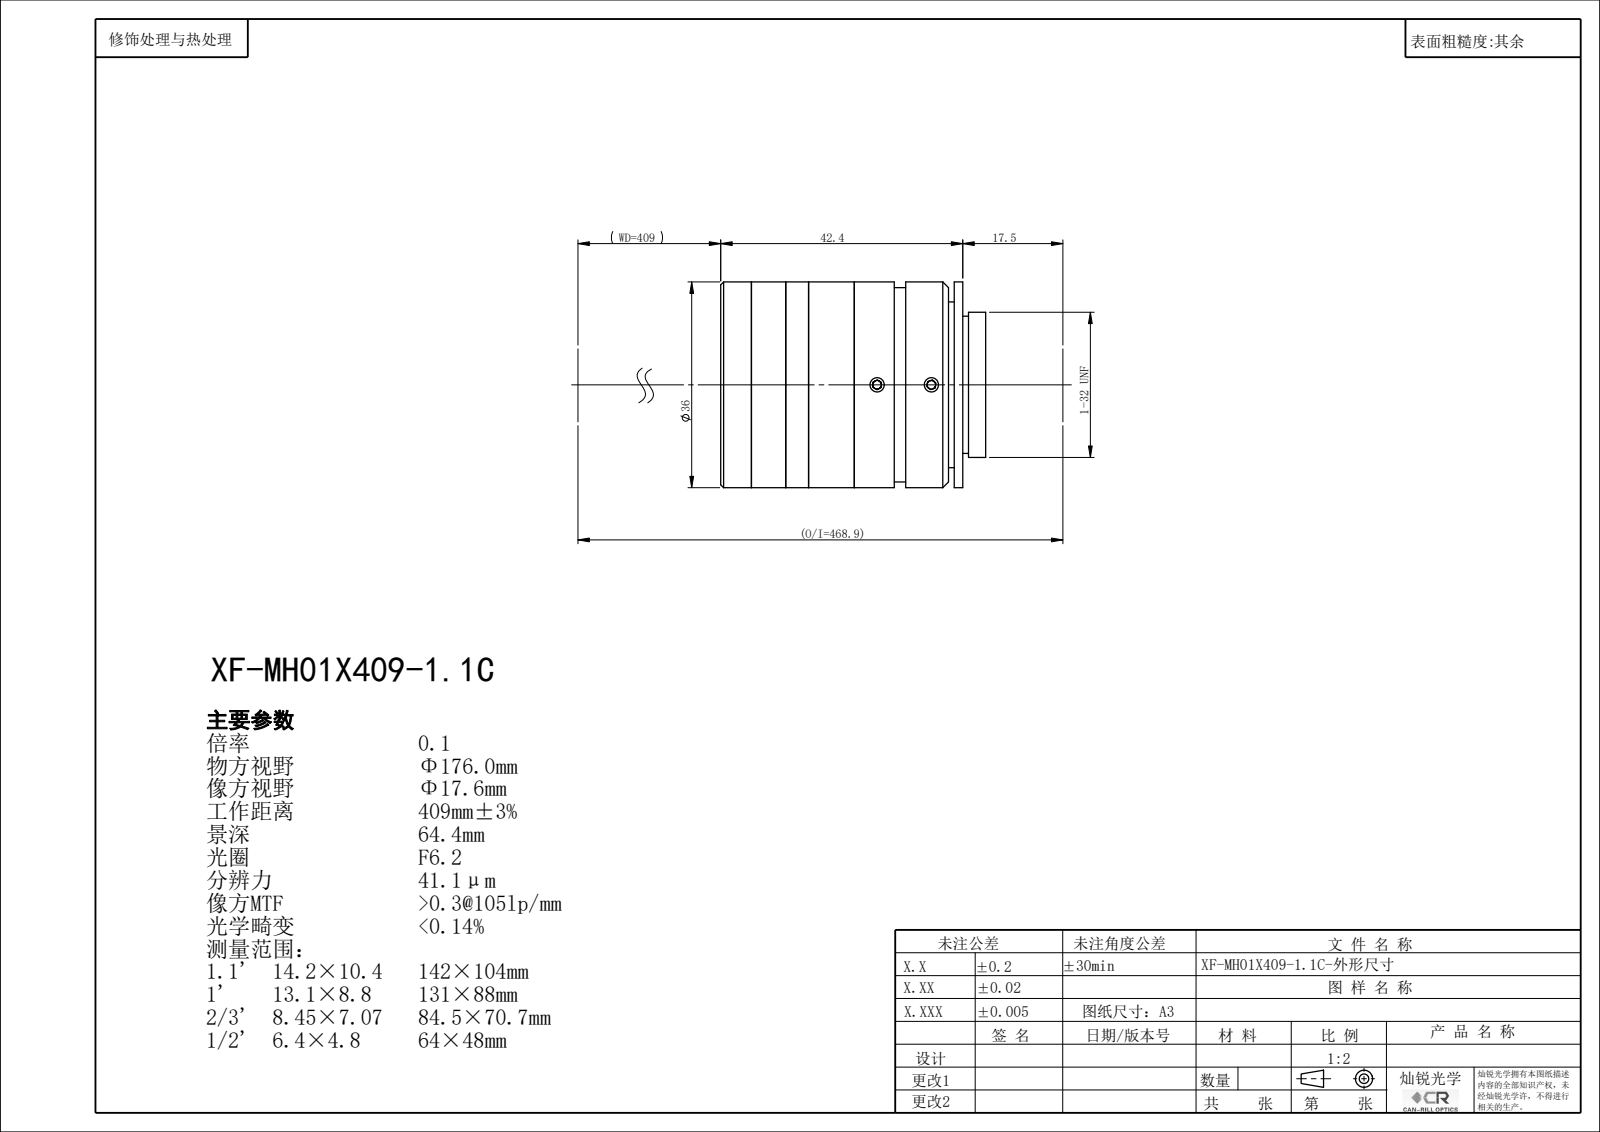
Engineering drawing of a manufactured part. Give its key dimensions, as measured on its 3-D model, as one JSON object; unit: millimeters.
{"part_name": "XF-MH01X409-1.1C", "step_written_by": "SolidWorks 2022 (CONFIG_CONTROL_DESIGN)", "units": "millimeters", "bodies": {"solids": 0, "faces": 137, "planar": 71, "cylindrical": 46, "other": 20}, "overall_size": [46.38, 36, 36], "round_holes": [[2.5, 6], [15, 1], [17.4, 1], [22.4, 1], [24, 1], [24.9, 1], [26, 1], [26.4, 1]], "round_bosses_or_shafts": [[36, 1], [34, 1], [25.4, 1]], "face_to_face_distances": [42.37, 1.5, 40.87, 15.38, 25.49, 26.99, 29.38, 14, 11.49, 12.99], "hole_center_spacings": [9.5]}
